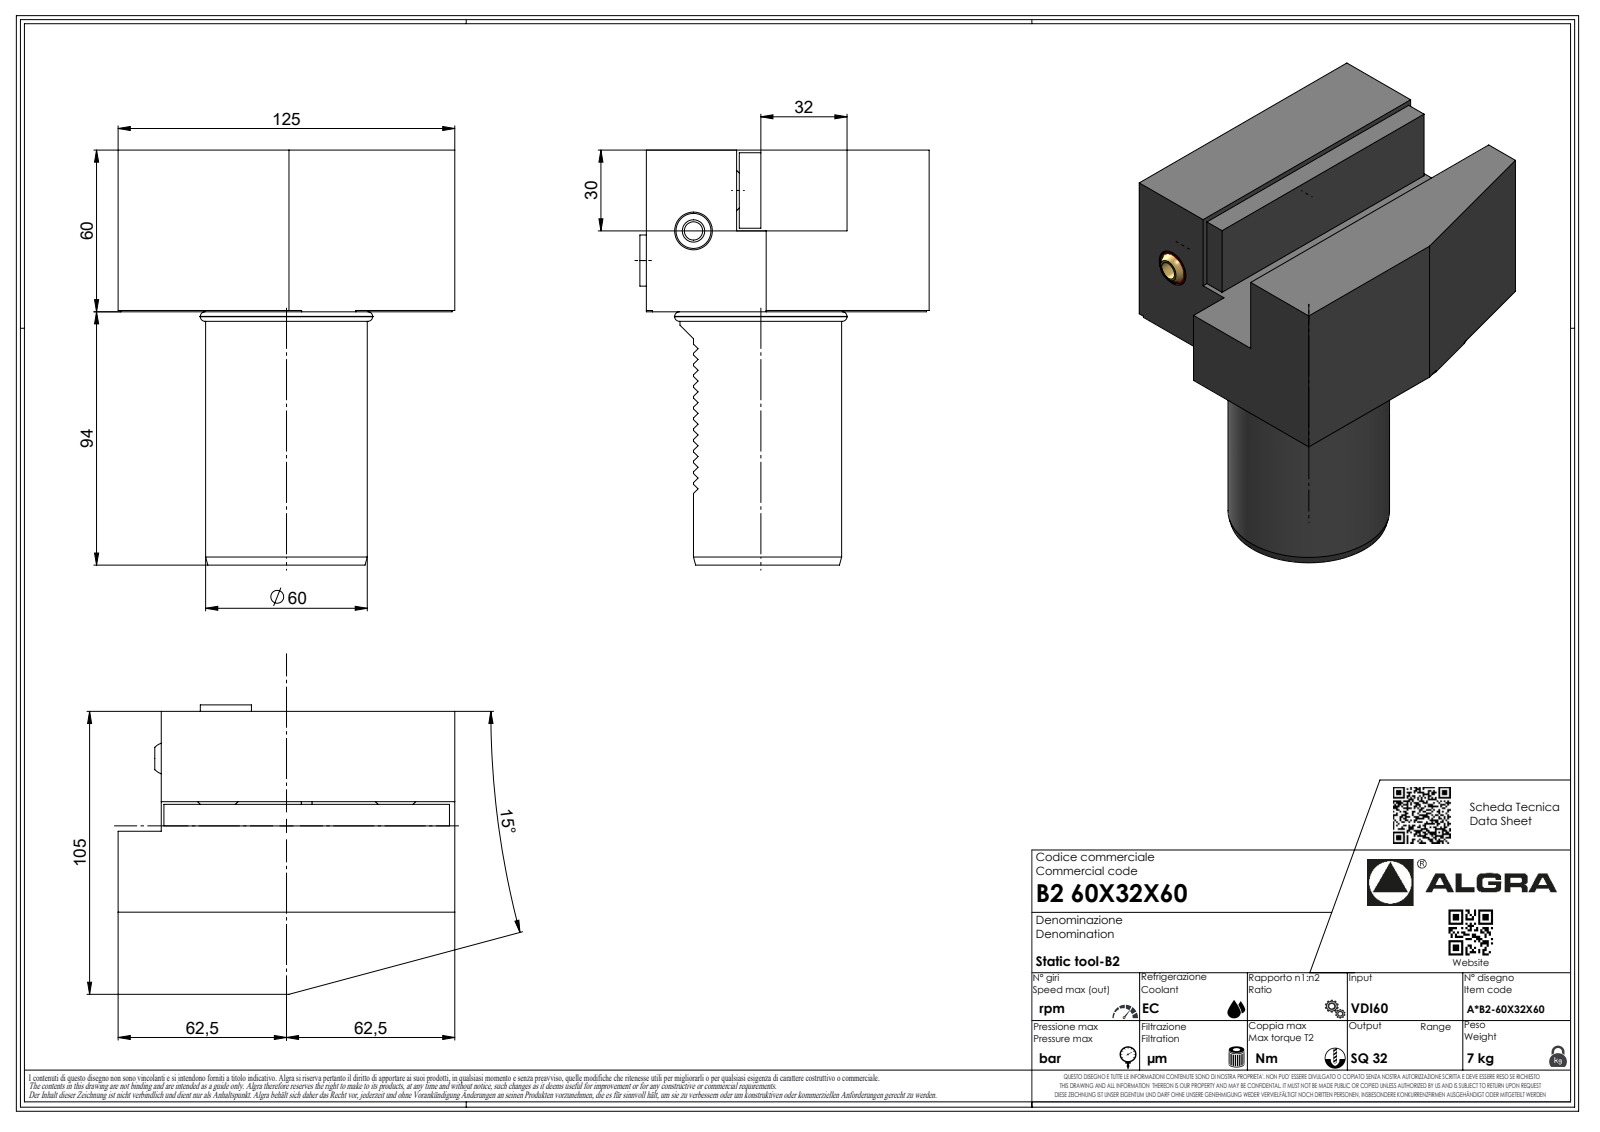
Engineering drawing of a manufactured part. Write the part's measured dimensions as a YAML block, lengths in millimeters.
part_name: "B260X32X60"
step_written_by: "SolidWorks 2023 (AUTOMOTIVE_DESIGN)"
units: millimeters
bodies: {solids: 1, faces: 349, planar: 236, cylindrical: 33, other: 80}
overall_size: [154, 125, 107.4]
volume: 848031
surface_area: 75939
round_holes:
  - {diameter: 2.1, count: 1}
round_bosses_or_shafts:
  - {diameter: 64.19, count: 1}
  - {diameter: 60, count: 1}
  - {diameter: 19, count: 1}
  - {diameter: 6.37, count: 1}
  - {diameter: 1.7, count: 1}
partial_cylinders:
  - {radius: 0.33, count: 7}
  - {radius: 0.52, count: 7}
  - {radius: 3.7, count: 7}
  - {radius: 0.21, count: 1}
  - {radius: 61.5, count: 1}
face_to_face_distances: [30, 60, 30.5, 105, 74.5, 125, 62.5, 32, 42.5, 154]
